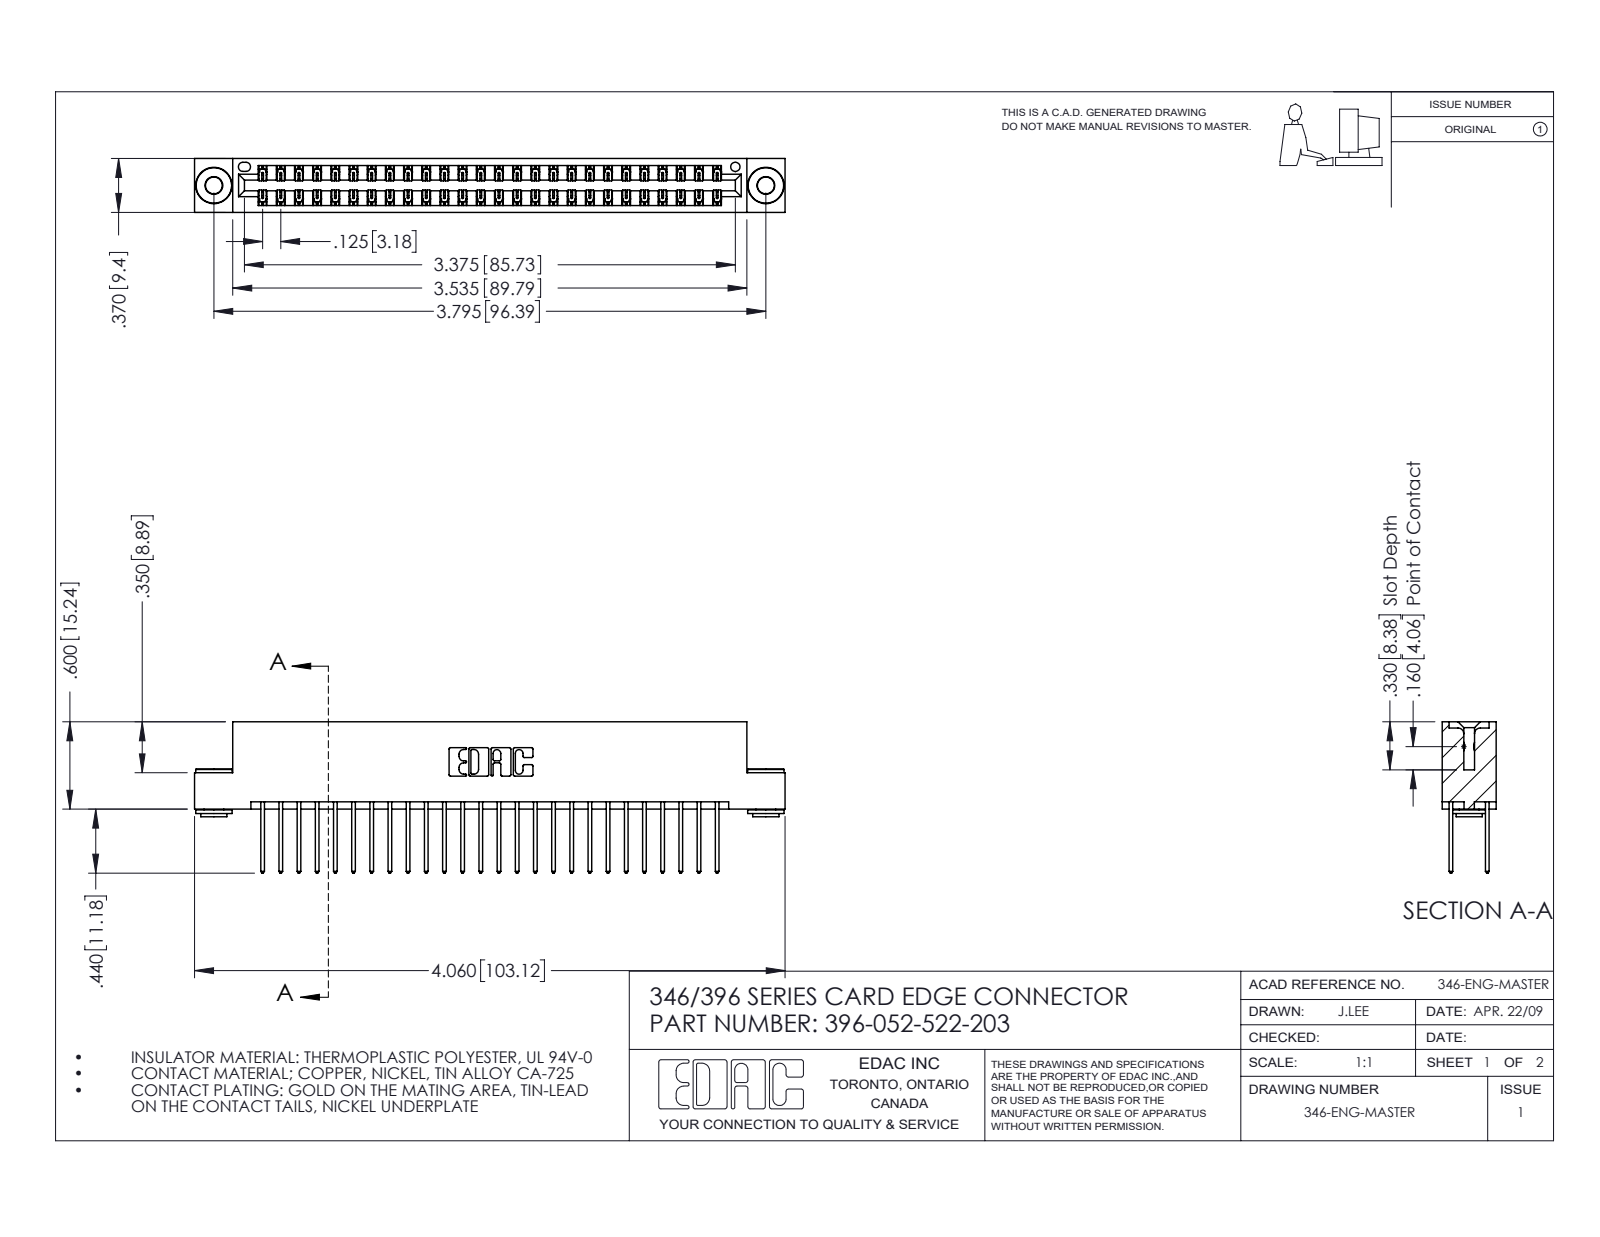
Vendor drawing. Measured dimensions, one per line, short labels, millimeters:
name: 345-250-002_345-250-002-102; 346 Part_Flush Mounting Lugs - 0.156 Dia-TH; 396-052-522-203; 345-292-001_345-293-122
written by: SolidWorks 2016 (CONFIG_CONTROL_DESIGN)
unit: mm
bodies: 55 solids, 2864 faces (1906 planar, 950 cylindrical, 8 other)
size: 103.1 × 26.4 × 9.4
volume: 10 100 mm³; area: 14 440 mm²
holes: 2× ⌀2.9, 2× ⌀4, 1× ⌀1.6
bosses: 2× ⌀6.4, 2× ⌀4.6, 2× ⌀3.5
rounds: 78× R0.2, 52× R0.3, 22× R0.3, 6× R0.2, 6× R0.8, 3× R0.7, 2× R0.4, 2× R0.6
face distances: 1.2, 8.2, 6.4, 9.4, 0.6, 1.8, 7.6, 7, 3.8, 5.6
hole spacings: 6.2, 91.1, 96.4
